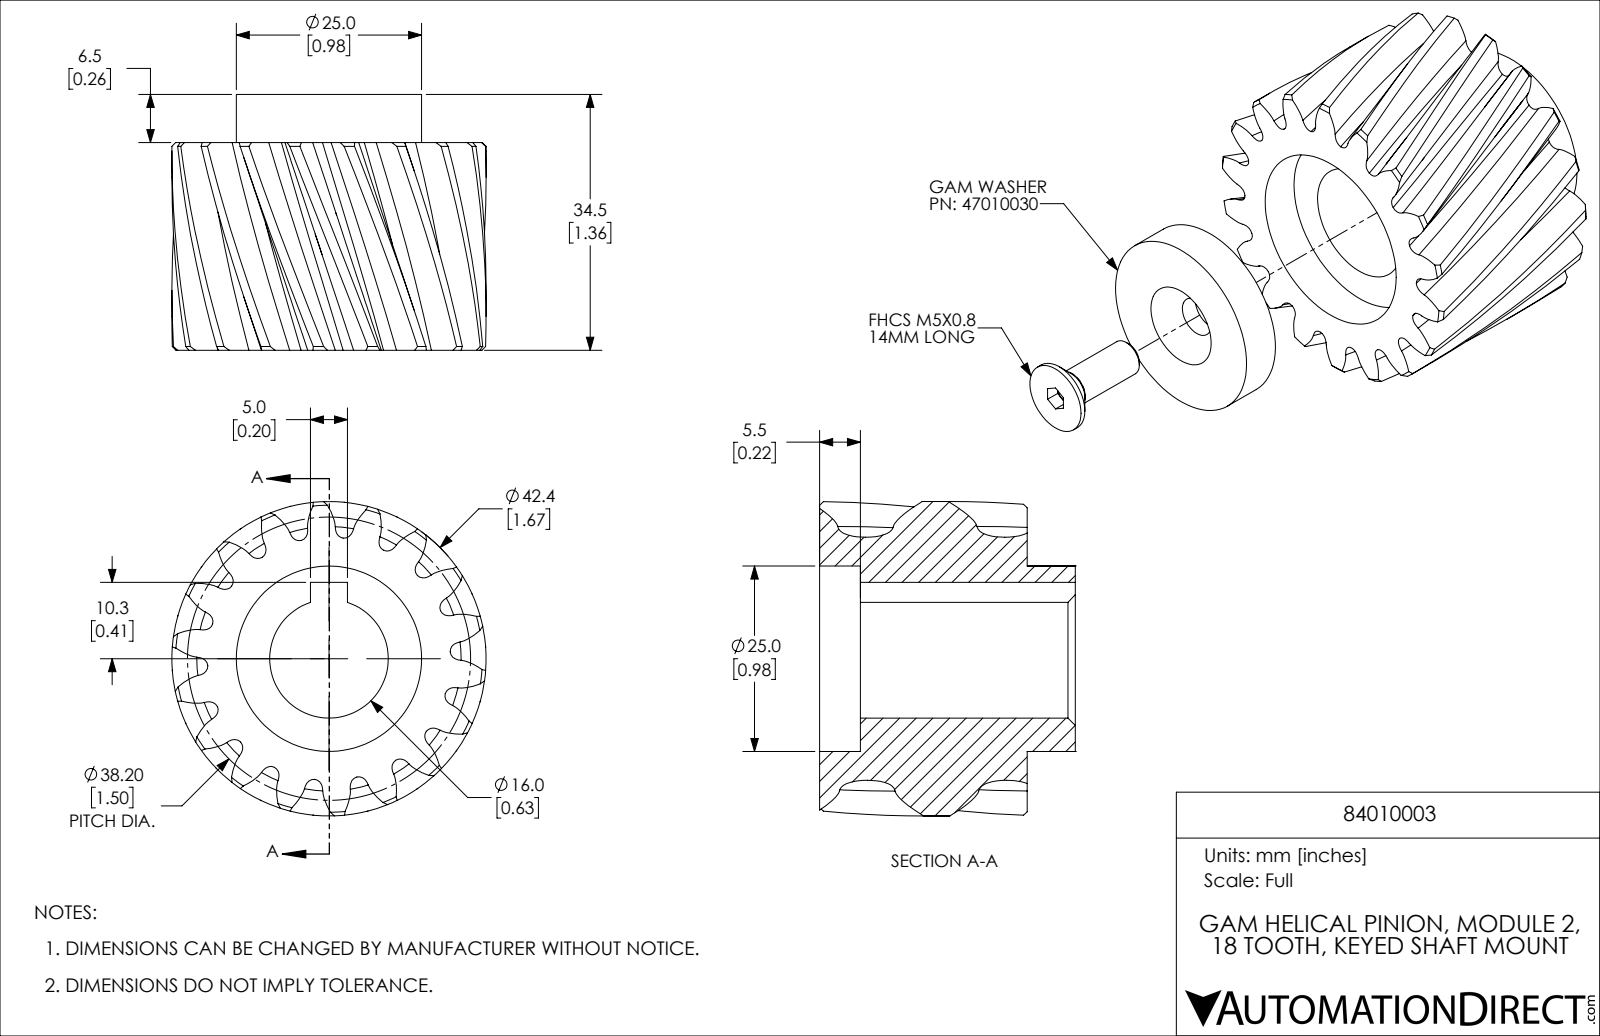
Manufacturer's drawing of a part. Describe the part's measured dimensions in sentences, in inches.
The part is named "84010003". Its 3-D file was written by "SolidWorks 2019 (CONFIG_CONTROL_DESIGN)". It is 3 solids with 179 faces: 23 planar, 35 cylindrical and 121 other. Overall it measures 1.669 by 1.669 by 1.358 inches. Its volume is 1.745 cubic inches and its surface area 20.01 square inches. Round holes: 1 of diameter 0.217, 1 of diameter 0.63. Round bosses or shafts: 1 of diameter 1.669, 1 of diameter 0.984, 1 of diameter 0.384, 1 of diameter 0.197. The main face-to-face distances are 0.217, 1.102, 0.886, 1.358, 1.142, 0.256, 0.197, 0.551, 0.335, 0.807.
